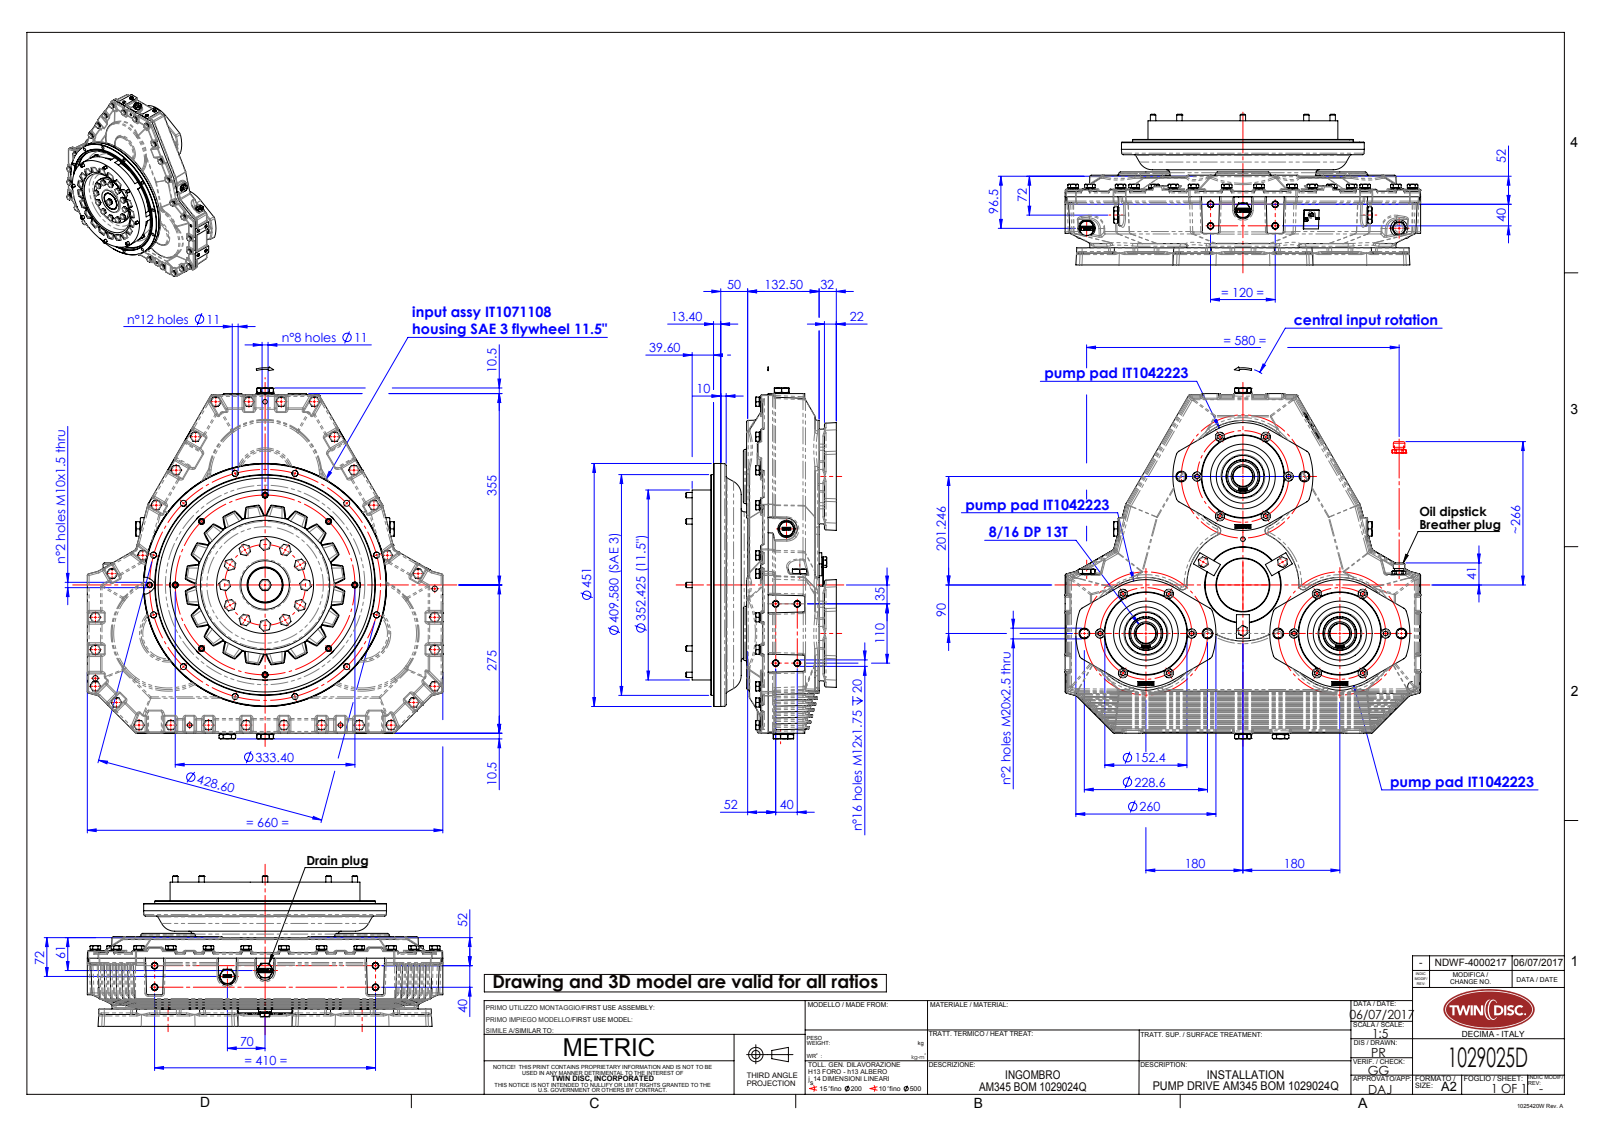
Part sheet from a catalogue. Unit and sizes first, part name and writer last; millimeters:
Units: millimetres
Overall size (bounding box): 690.04 × 660 × 279.5
Round holes (diameter × count): ⌀11 ×53, ⌀10.2 ×52, ⌀10.5 ×38, ⌀8.5 ×37, ⌀13 ×19, ⌀17 ×18, ⌀10 ×12, ⌀12 ×12, ⌀12.2 ×7, ⌀17.5 ×6, ⌀18.5 ×4, ⌀80 ×4
Round bosses / shafts (diameter × count): ⌀10 ×59, ⌀16.2 ×41, ⌀18.1 ×33, ⌀18 ×19, ⌀12 ×19, ⌀16 ×18, ⌀24 ×12, ⌀21 ×8
Partial cylindrical surfaces — rounded edges, fillets, slot ends (radius × count): R3 ×405, R2 ×126, R1.5 ×108, R5 ×98, R2.5 ×80, R0.45 ×58, R10.97 ×12, R16 ×4
Main face-to-face distances: 20, 10, 182.5, 30, 32, 48, 18, 152.5, 53, 40
Hole centre spacings: 57.4, 120, 138.58, 40, 207.84, 51.37, 66.61, 85.42
Volume: 10 400 000 mm³ · Surface area: 3 568 000 mm²
Bodies: 37 solids, 10027 faces (4169 planar, 2520 cylindrical, 3338 other)
Part name (STEP PRODUCT): IT4588040_rev00-installation; IT0000198_rev00-installation; ITB00610000_rev02-installation; IT1071108_rev01-installation (+5 more)
STEP written by: SolidWorks 2015 (CONFIG_CONTROL_DESIGN)
